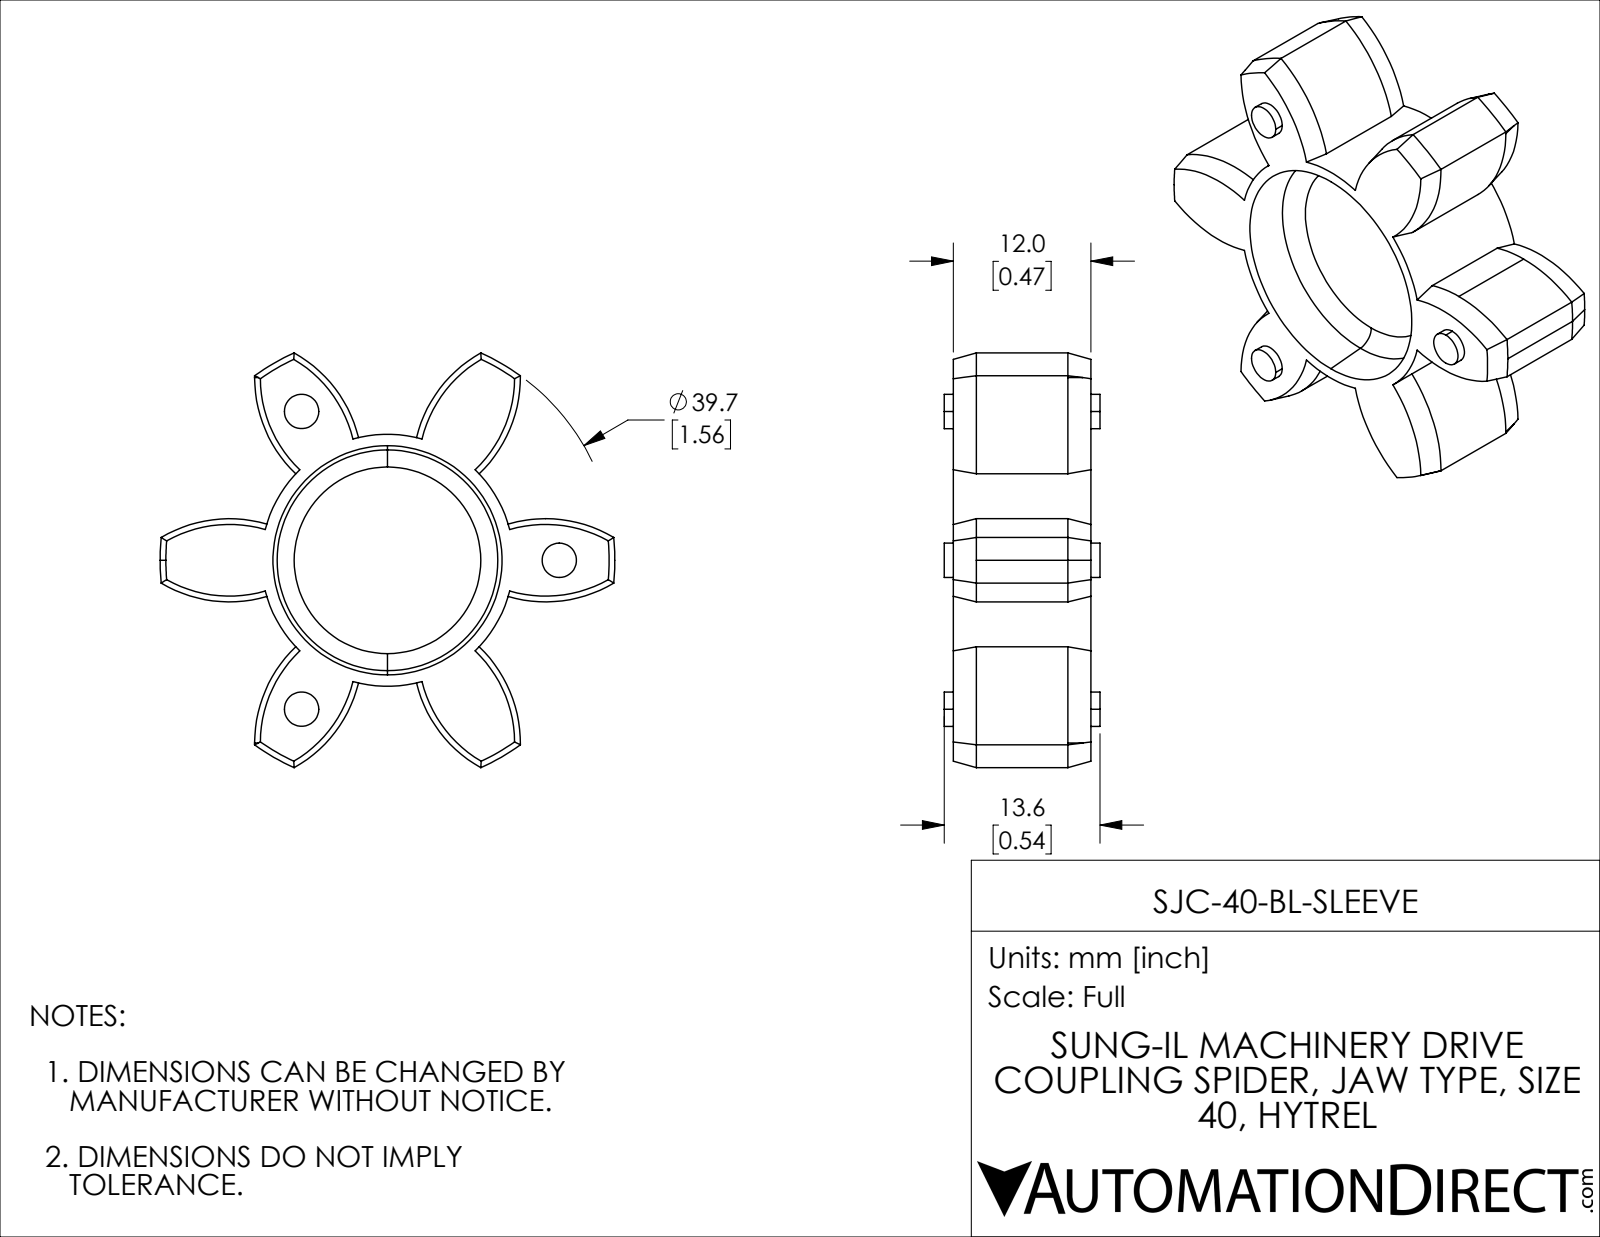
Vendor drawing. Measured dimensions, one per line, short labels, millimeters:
name: SJC-40-BL-SLEEVE
written by: SolidWorks 2021 (CONFIG_CONTROL_DESIGN)
unit: mm
bodies: 1 solid, 99 faces (10 planar, 39 cylindrical, 50 other)
size: 39.7 × 36.2 × 13.6
volume: 5 685 mm³; area: 3 895 mm²
bosses: 6× ⌀3
rounds: 6× R11.6, 1× R11, 1× R19.85
face distances: 5, 7, 12, 2, 0.8, 5.8, 7.8, 12.8, 13.6
